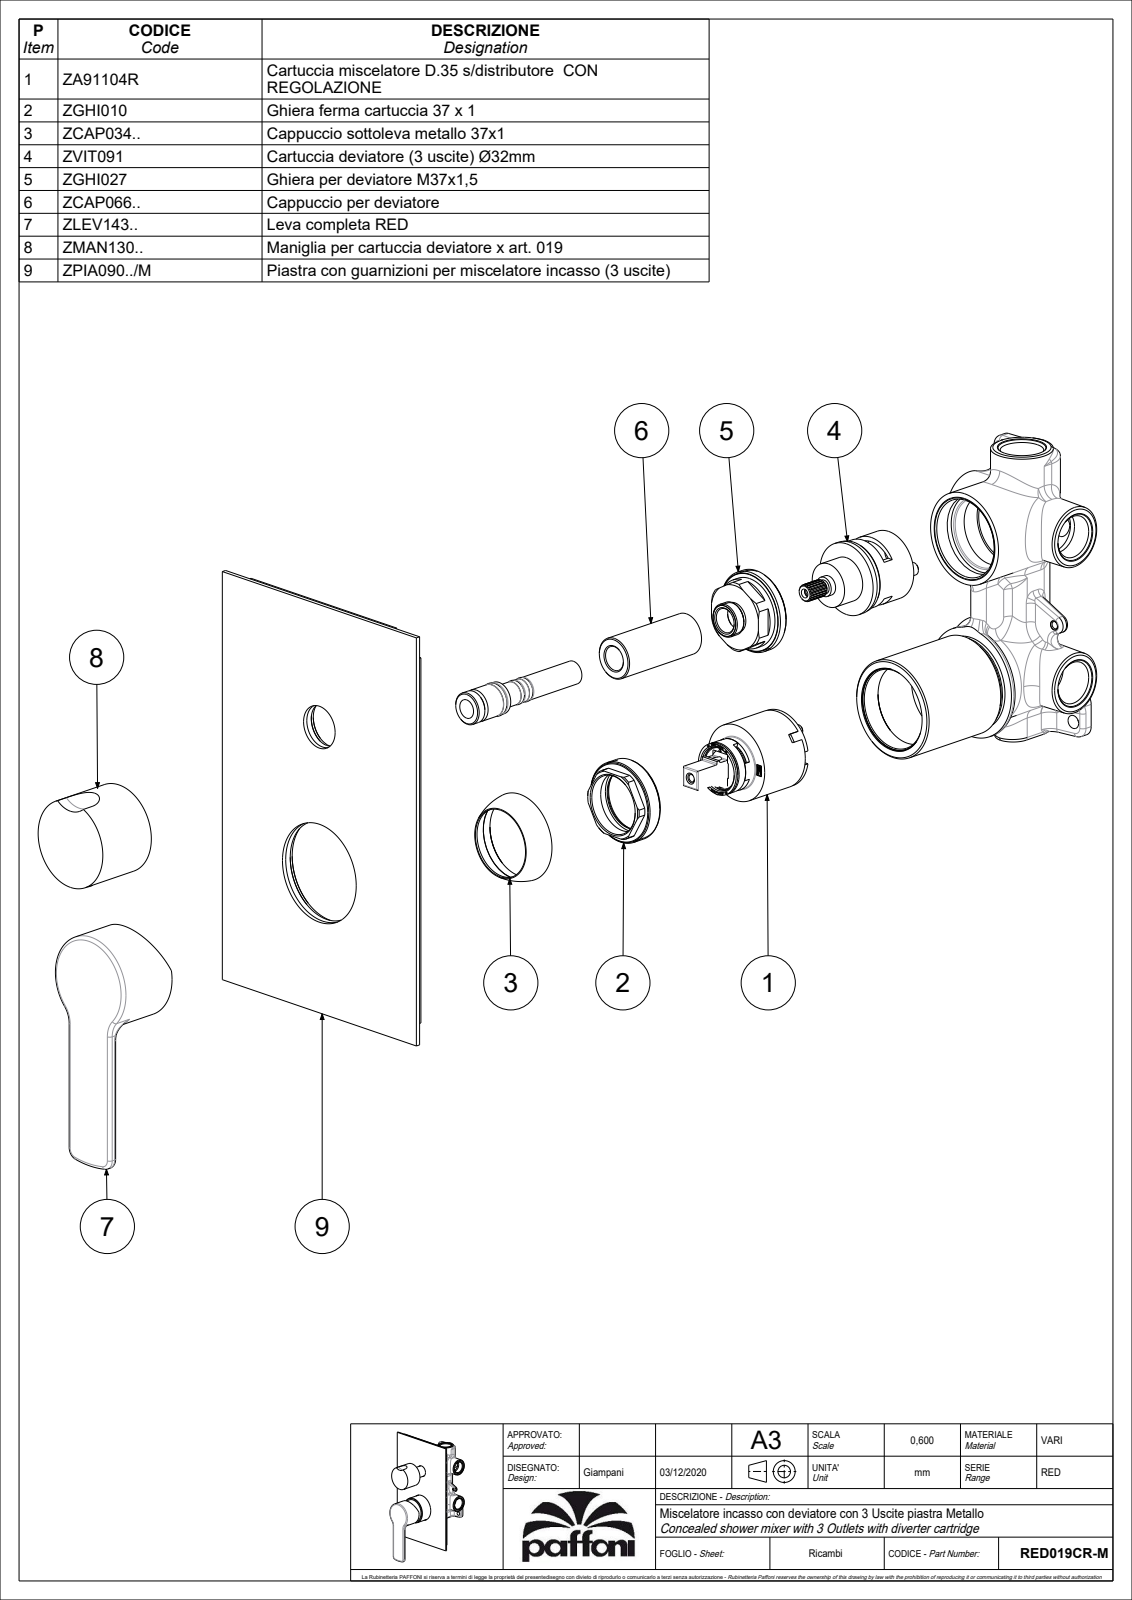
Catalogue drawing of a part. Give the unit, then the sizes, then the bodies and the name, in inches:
Units: inches
Overall size (bounding box): 8.268 × 4.724 × 2.356
Round holes (diameter × count): ⌀0.118 ×2, ⌀0.13 ×2, ⌀0.157 ×2, ⌀0.177 ×2, ⌀0.768 ×2, ⌀1.417 ×2, ⌀0.126 ×1, ⌀0.165 ×1, ⌀0.197 ×1, ⌀0.433 ×1, ⌀0.583 ×1, ⌀0.783 ×1
Round bosses / shafts (diameter × count): ⌀0.299 ×2, ⌀0.217 ×2, ⌀1.764 ×1, ⌀1.693 ×1, ⌀1.575 ×1, ⌀1.378 ×1, ⌀0.945 ×1, ⌀0.925 ×1
Partial cylindrical surfaces — rounded edges, fillets, slot ends (radius × count): R0.02 ×45, R0.006 ×11, R0.012 ×4, R0.059 ×4, R0.039 ×2, R0.197 ×2, R0.394 ×2, R0.276 ×1
Main face-to-face distances: 0.079, 2.169, 2.091, 0.177, 2.346, 2.268, 0.354, 0.689, 0.217, 2.185
Hole centre spacings: 0.091, 0.394, 0.492, 0.583, 2.677, 3.071
Volume: 7.558 in³ · Surface area: 147.3 in²
Bodies: 4 solids, 1097 faces (590 planar, 285 cylindrical, 222 other)
Part name (STEP PRODUCT): RED018CR-M
STEP written by: CREO PARAMETRIC BY PTC INC, 2020044 (CONFIG_CONTROL_DESIGN)
